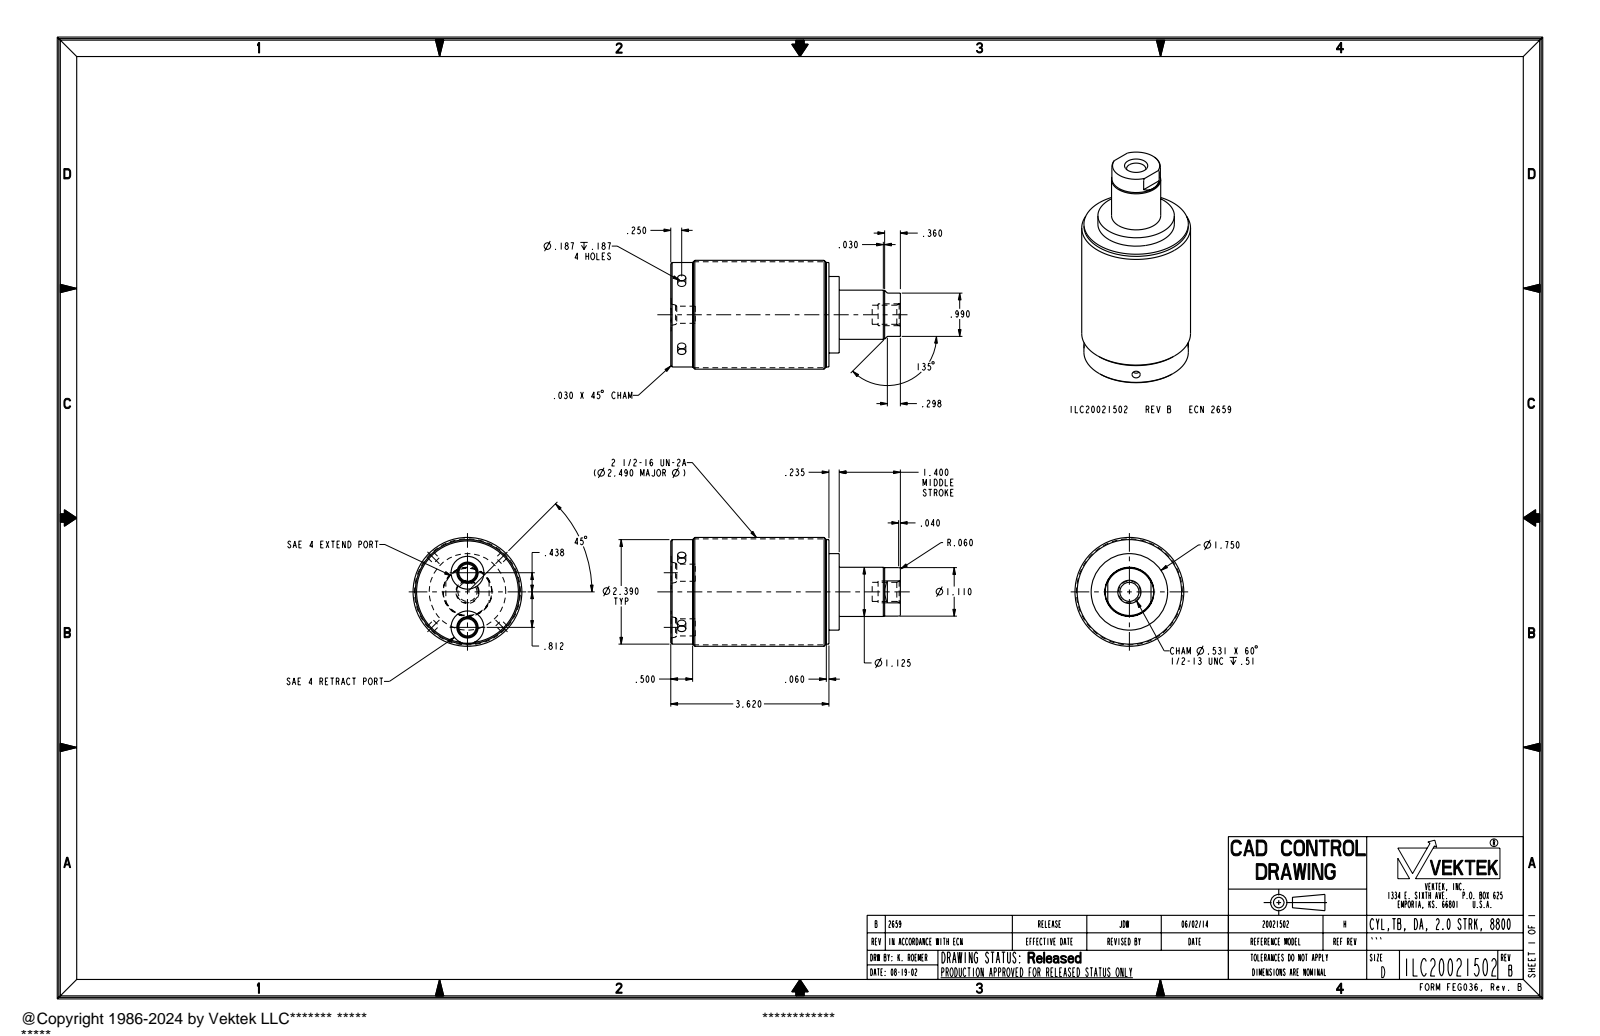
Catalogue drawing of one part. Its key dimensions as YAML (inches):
part_name: "ILC20021502"
step_written_by: "PRO/ENGINEER BY PARAMETRIC TECHNOLOGY CORPORATION, 2013320 (AUTOMOTIVE_DESIGN)"
units: inches
bodies: {solids: 1, faces: 71, planar: 18, cylindrical: 33, other: 20}
overall_size: [5.255, 2.49, 2.49]
volume: 19.05
surface_area: 69.9
round_holes:
  - {diameter: 0.187, count: 4}
  - {diameter: 0.392, count: 2}
  - {diameter: 0.75, count: 2}
  - {diameter: 0.437, count: 1}
round_bosses_or_shafts:
  - {diameter: 2.49, count: 1}
  - {diameter: 2.424, count: 1}
  - {diameter: 2.39, count: 1}
  - {diameter: 1.75, count: 1}
  - {diameter: 1.125, count: 1}
  - {diameter: 1.11, count: 1}
  - {diameter: 0.5, count: 1}
face_to_face_distances: [3.62, 0.235, 3.855, 1.4, 1.635, 5.255, 5.245, 3.845, 3.61, 4.695]
hole_center_spacings: [0.438, 0.812, 1.25]
